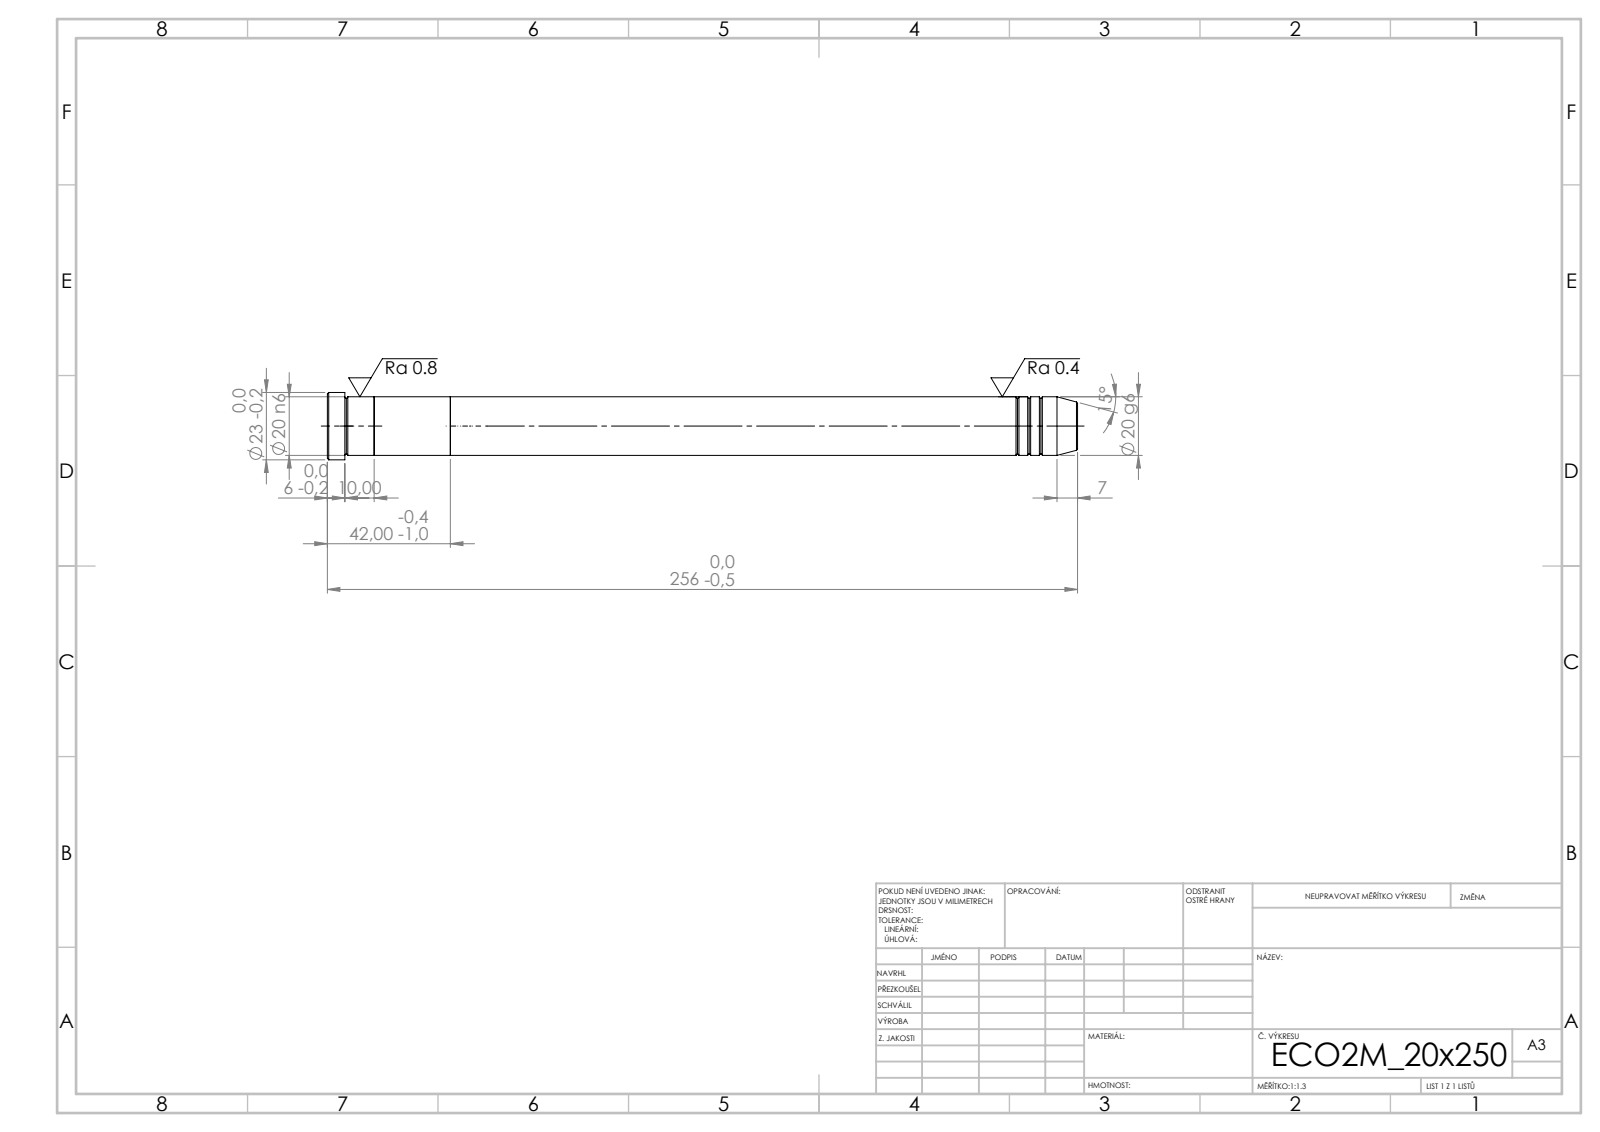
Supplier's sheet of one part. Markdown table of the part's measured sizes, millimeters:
| quantity | value |
| --- | --- |
| STEP written by | SolidWorks 2019 (CONFIG_CONTROL_DESIGN) |
| units | millimeters |
| bodies | 3 solids, 43 faces (7 planar, 14 cylindrical, 22 other) |
| overall size | 256 × 23 × 23 |
| volume | 80 539 mm³ |
| surface area | 18 199 mm² |
| round bosses / shafts (diameter × count) | 23 × 1, 20 × 1 |
| main face-to-face distances | 26, 42, 16, 214, 240, 256, 250, 36, 10, 6 |
